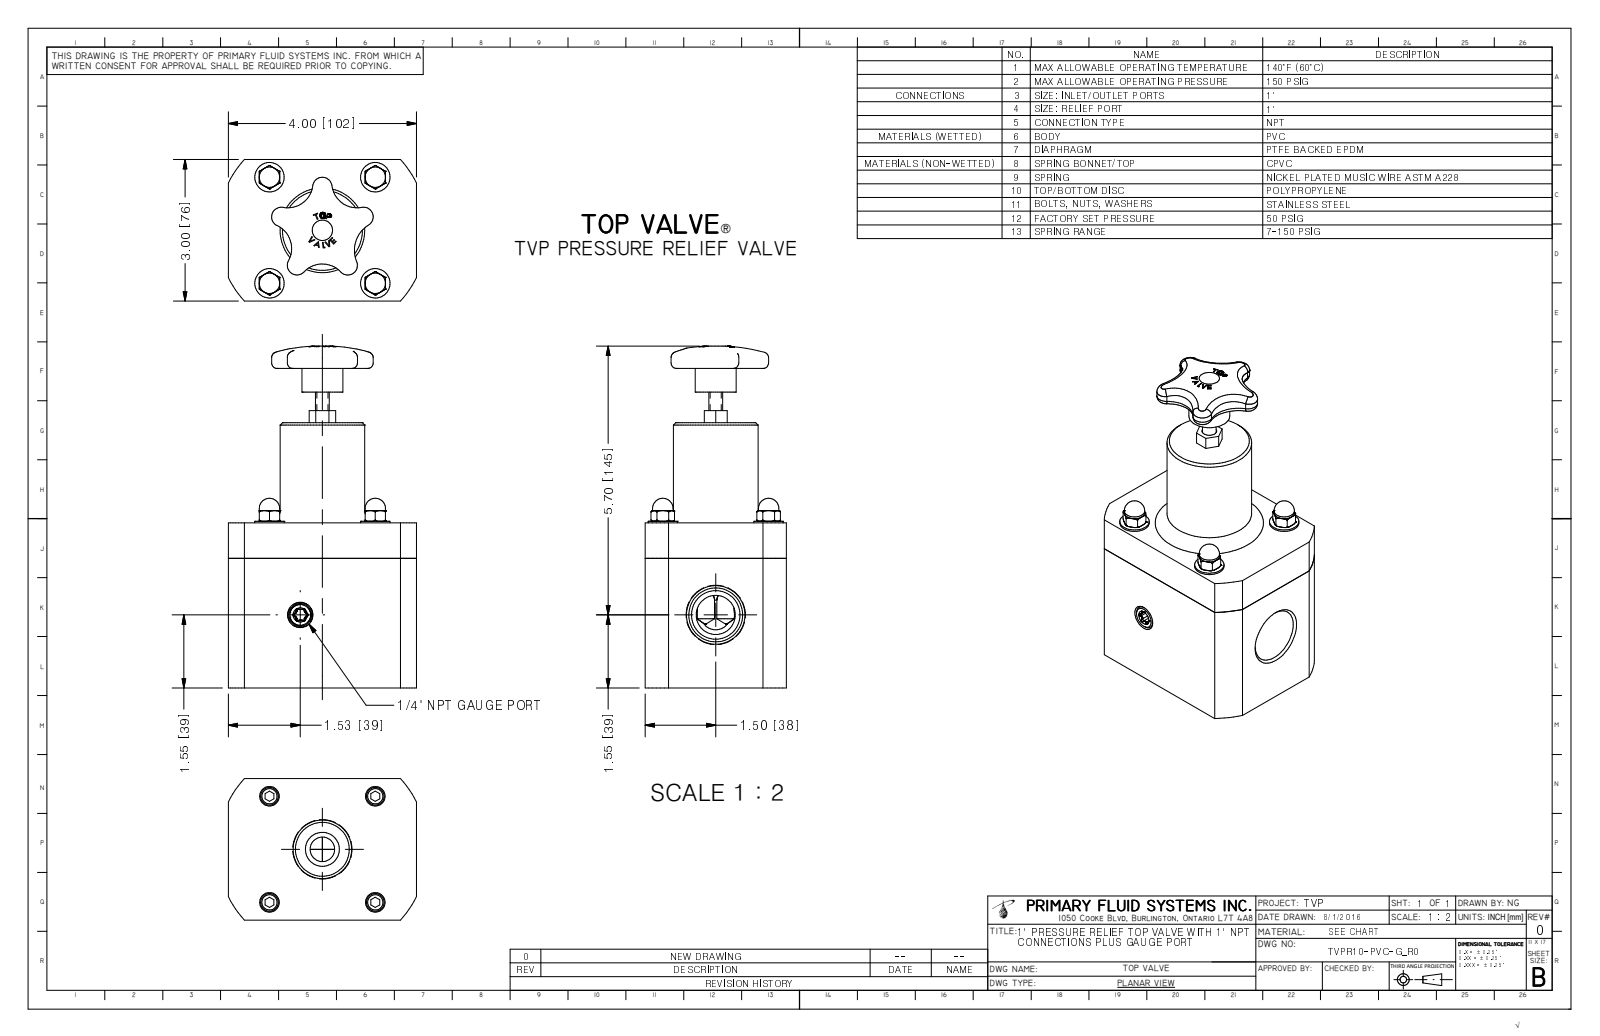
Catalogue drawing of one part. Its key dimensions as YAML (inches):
part_name: "TVPR10-PVC-G_R0"
step_written_by: "Autodesk Inventor 2009 (AUTOMOTIVE_DESIGN)"
units: inches
bodies: {solids: 1, faces: 366, planar: 155, cylindrical: 54, other: 157}
overall_size: [7.25, 4, 3]
volume: 44.88
surface_area: 108.7
round_holes:
  - {diameter: 0.175, count: 4}
  - {diameter: 1.144, count: 2}
  - {diameter: 2.525, count: 1}
round_bosses_or_shafts:
  - {diameter: 0.625, count: 4}
  - {diameter: 0.433, count: 4}
  - {diameter: 0.375, count: 4}
  - {diameter: 2.5, count: 1}
  - {diameter: 1.8, count: 1}
  - {diameter: 0.87, count: 1}
  - {diameter: 0.293, count: 1}
partial_cylinders:
  - {radius: 0.027, count: 6}
  - {radius: 0.085, count: 5}
  - {radius: 0.205, count: 5}
  - {radius: 0.536, count: 4}
  - {radius: 0.656, count: 4}
  - {radius: 0.625, count: 1}
  - {radius: 0.745, count: 1}
  - {radius: 2.238, count: 1}
face_to_face_distances: [3, 3.5, 4, 5.625, 2.125, 1, 2, 0.875, 2.625, 4.75]
hole_center_spacings: [2.25, 1.591, 3.182, 1.591, 1.591]
